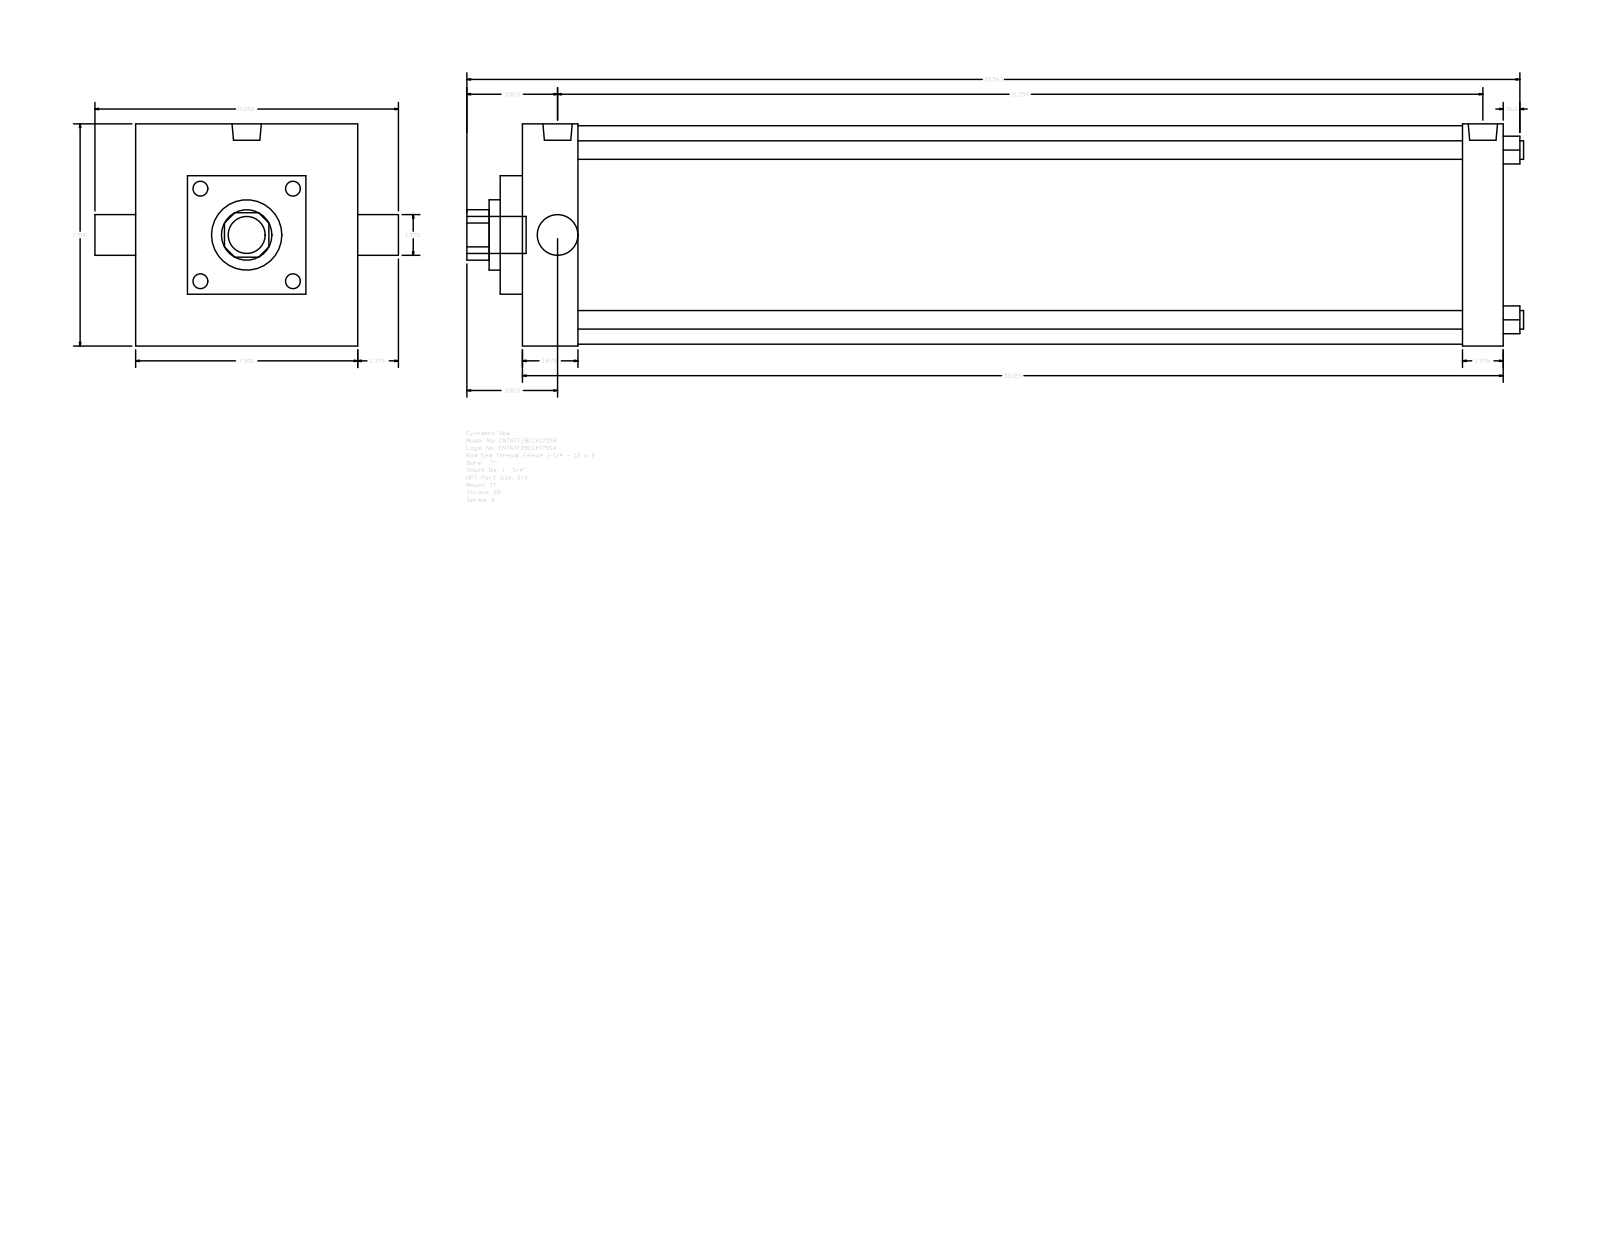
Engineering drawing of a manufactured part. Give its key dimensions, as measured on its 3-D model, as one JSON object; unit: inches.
{"part_name": "A_TF__0700_1.75", "step_written_by": "GSSL Pune (CONFIG_CONTROL_DESIGN)", "units": "inches", "bodies": {"solids": 0, "faces": 89, "planar": 65, "cylindrical": 24, "other": 0}, "overall_size": [35.687, 10.25, 7.5], "round_holes": [[0.625, 4], [1.375, 1], [1.75, 1], [2.375, 1], [7.375, 1]], "round_bosses_or_shafts": [[0.594, 3], [0.989, 2], [1.25, 1]], "partial_cylinders_radius": [[0.852, 1]], "face_to_face_distances": [7.5, 33.125, 1.75, 1.375, 0.75, 1.875, 31.25, 31.75, 29.875, 5.75], "hole_center_spacings": [4.052, 5.73, 8.103]}
